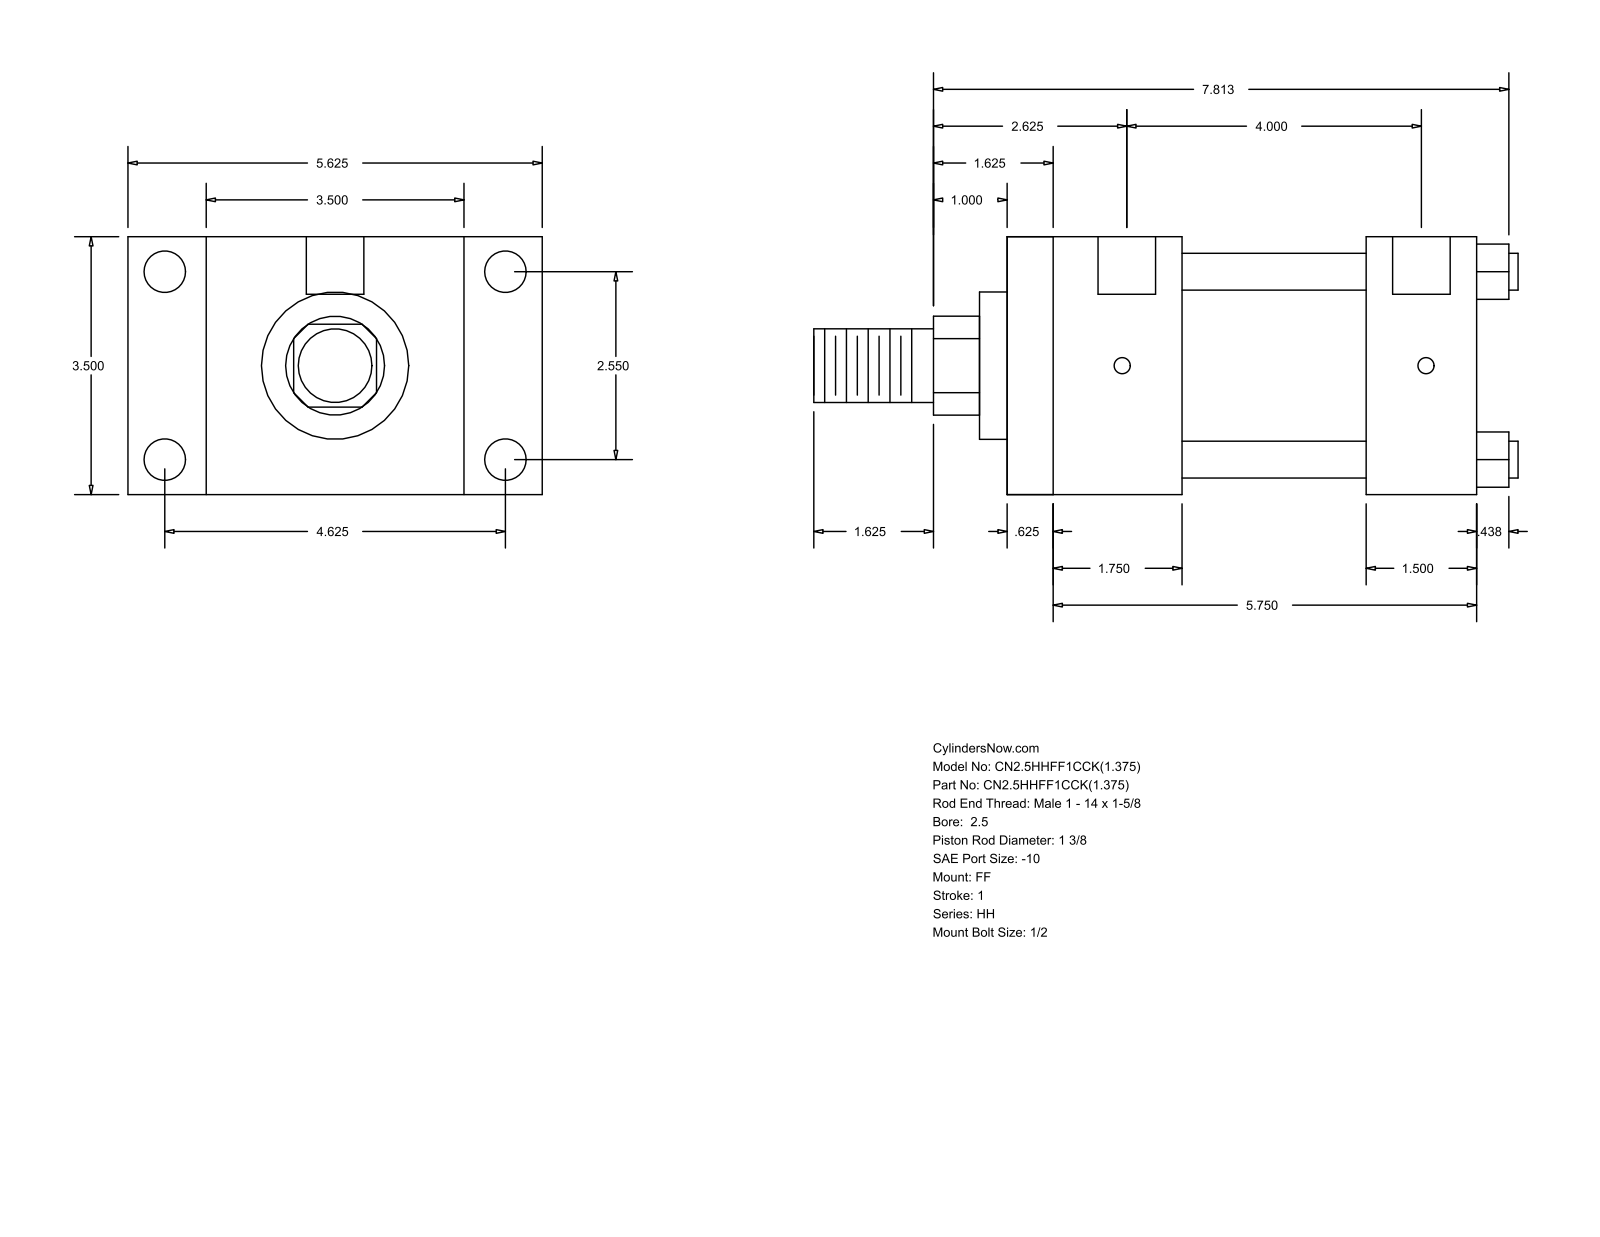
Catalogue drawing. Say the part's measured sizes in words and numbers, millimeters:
The part is named "HH_FF__0250_1.375". Its 3-D file was written by "GSSL Pune (CONFIG_CONTROL_DESIGN)". It is 0 solids with 92 faces: 64 planar, 28 cylindrical and 0 other. Overall it measures 242.89 by 142.88 by 88.9 millimeters. Round holes: 4 of diameter 5.56, 4 of diameter 14.3, 2 of diameter 19.84. Round bosses or shafts: 4 of diameter 12.7, 1 of diameter 73.03, 1 of diameter 50.8, 1 of diameter 34.92, 1 of diameter 25.4. Partial cylindrical surfaces (rounded edges, fillets, slot ends): 1 of radius 17.06. The main face-to-face distances are 88.9, 161.92, 15.87, 146.05, 115.89, 60.32, 44.45, 101.6, 123.82, 107.95. The hole center spacings are 1.58, 64.76, 103.19, 104.77, 117.48, 134.15, 101.61.
